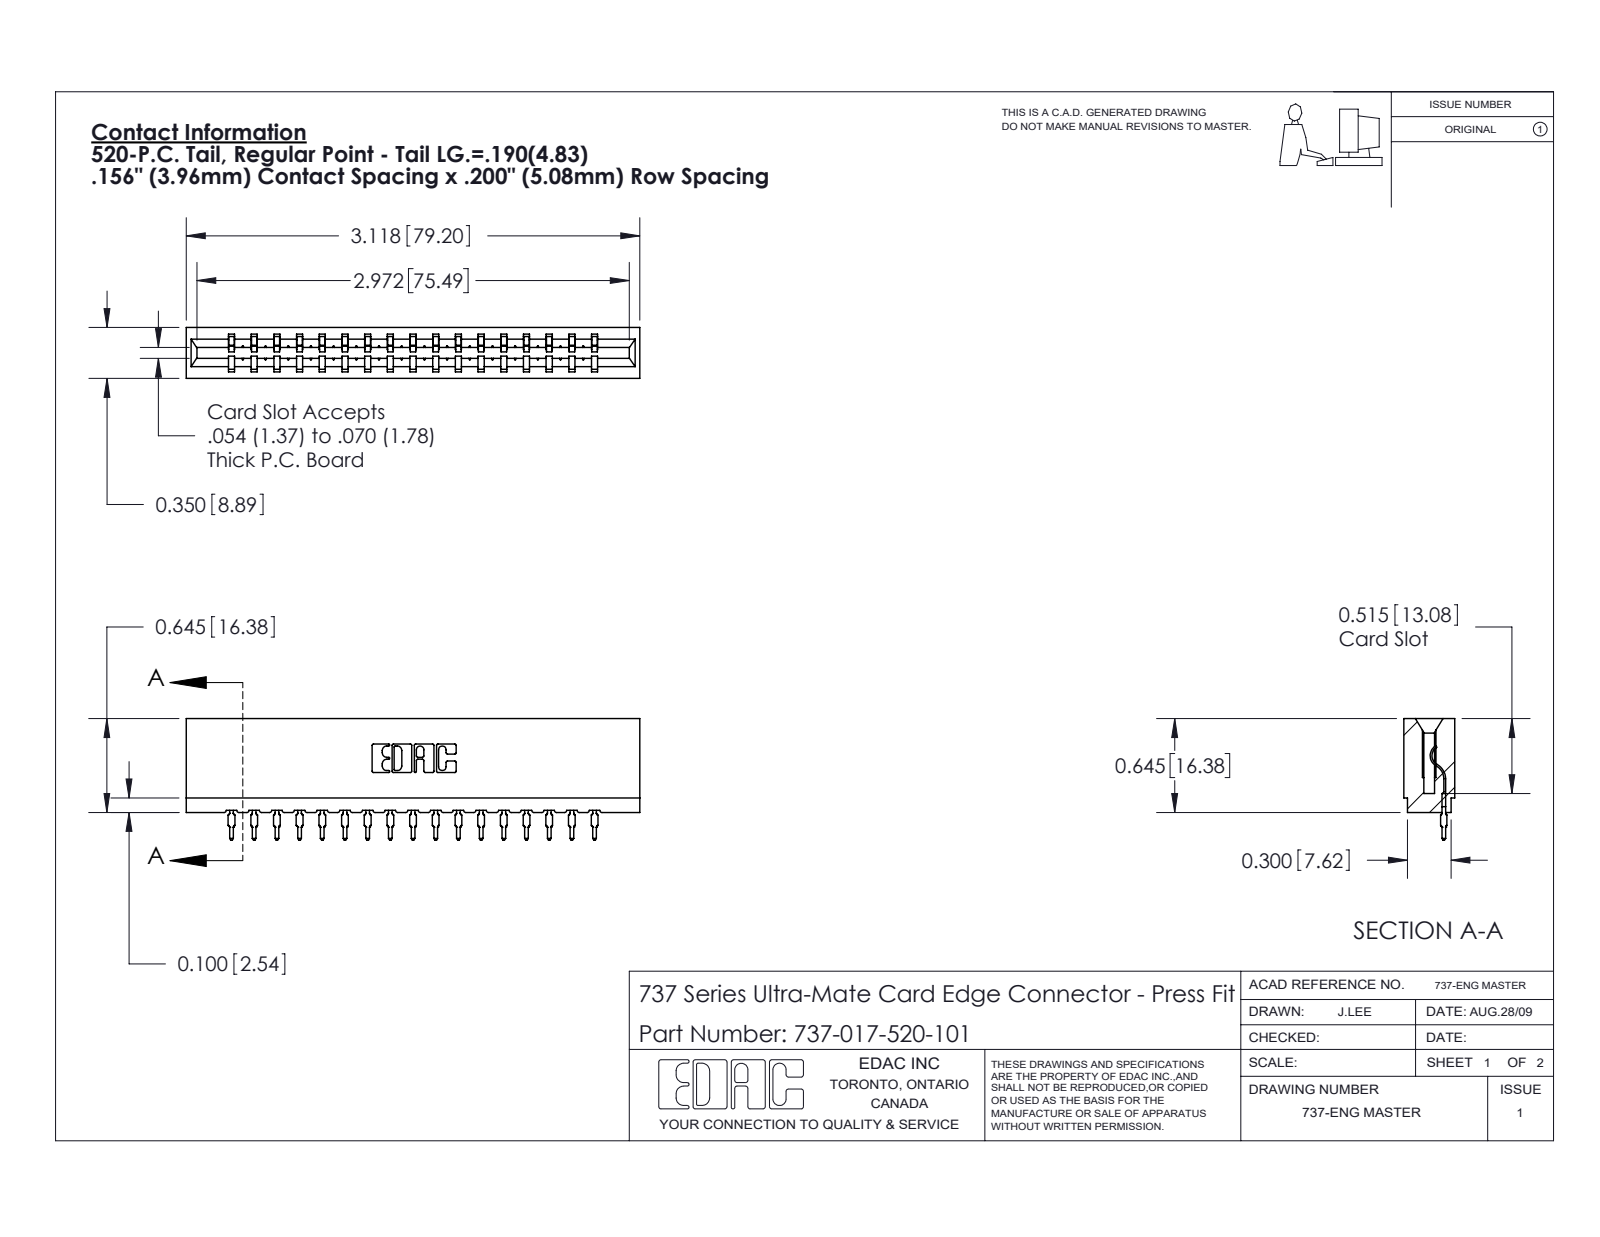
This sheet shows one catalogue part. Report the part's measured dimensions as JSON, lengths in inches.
{"part_name": "745-292-001_520; 737-017-520-101; 737 Part_Insulator Option - 01", "step_written_by": "SolidWorks 2020 (CONFIG_CONTROL_DESIGN)", "units": "inches", "bodies": {"solids": 18, "faces": 2015, "planar": 1210, "cylindrical": 363, "other": 442}, "overall_size": [3.118, 0.836, 0.35], "volume_in3": 0.476, "surface_area_in2": 15.36, "partial_cylinders_radius": [[0.015, 34], [0.021, 34], [0.01, 22], [0.007, 6], [0.031, 6], [0.005, 4], [0.011, 4], [0.026, 3]], "face_to_face_distances": [0.138, 0.212, 0.35, 0.156, 0.624, 0.78, 0.074, 0.468, 0.312, 0.045]}
